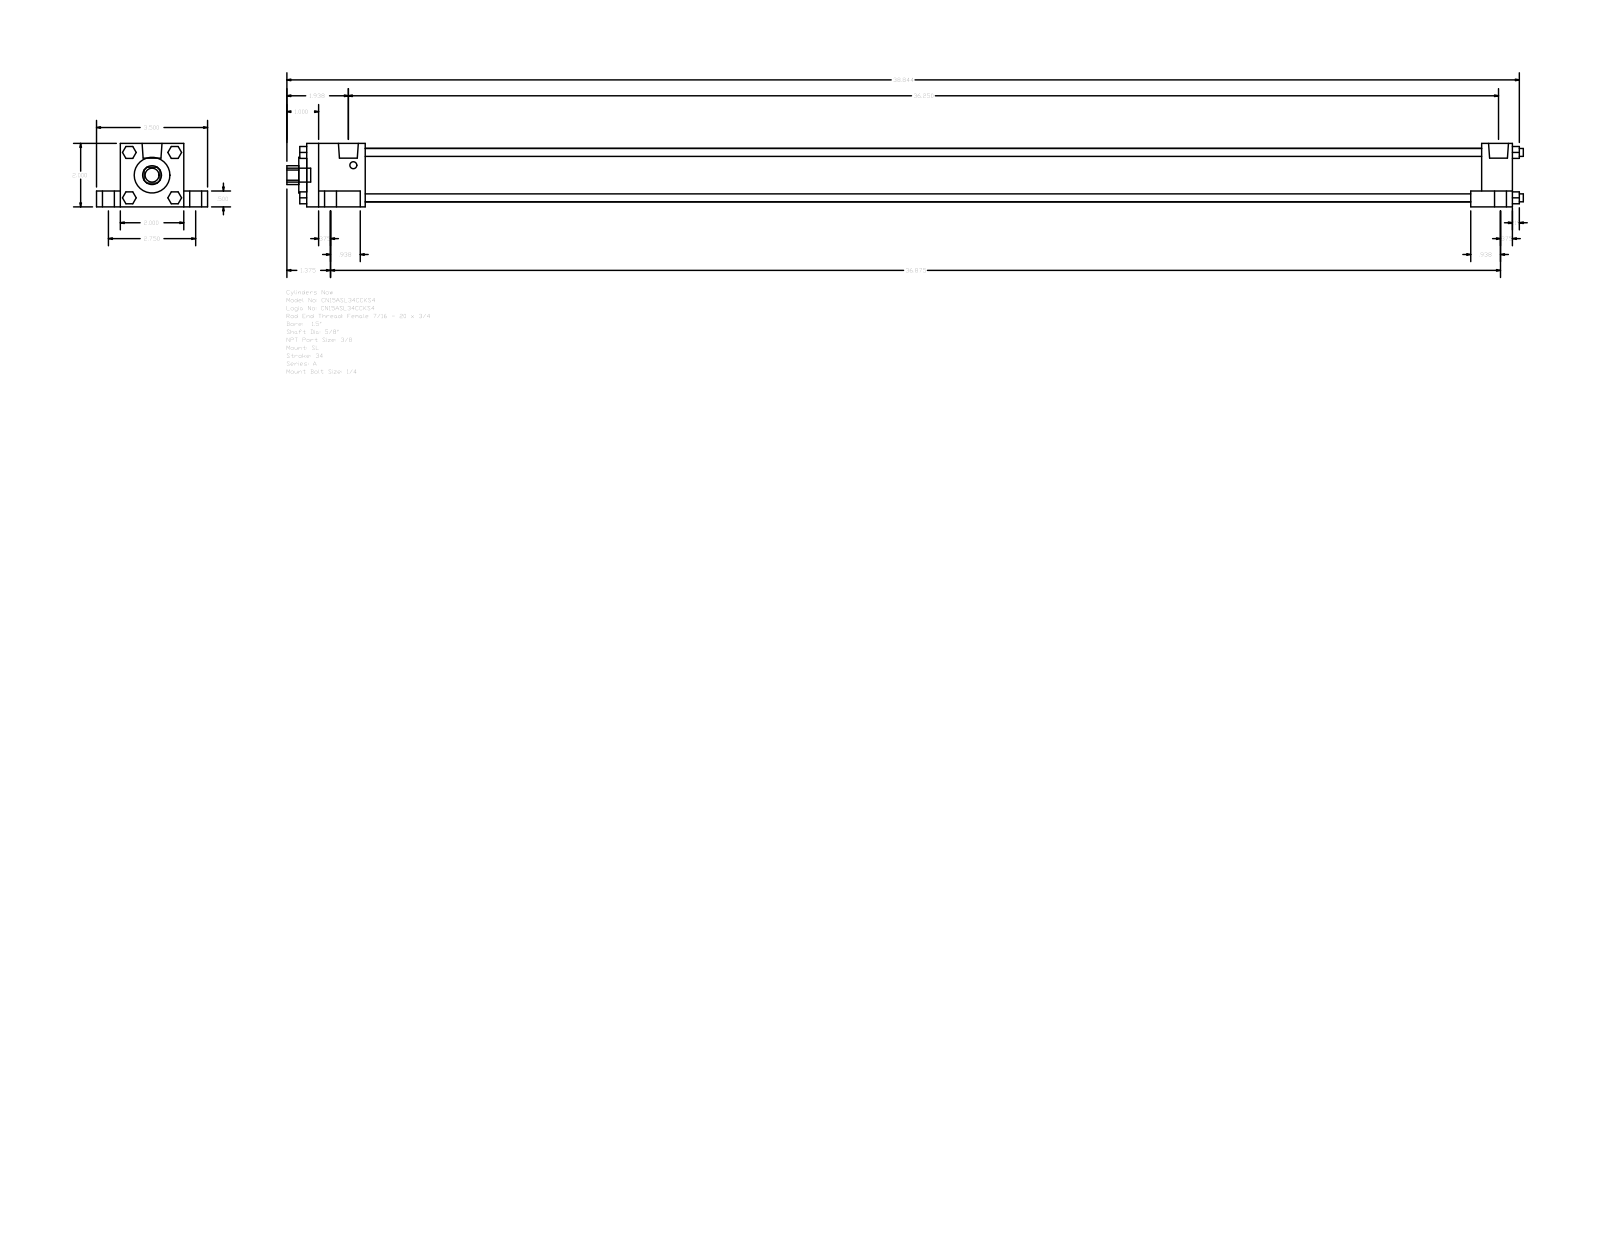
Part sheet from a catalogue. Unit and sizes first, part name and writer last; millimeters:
Units: millimetres
Overall size (bounding box): 989.81 × 88.9 × 50.8
Round holes (diameter × count): ⌀15.88 ×1, ⌀28.57 ×1, ⌀42.93 ×1
Round bosses / shafts (diameter × count): ⌀15.88 ×4, ⌀9.53 ×4, ⌀6.35 ×4, ⌀5.56 ×4, ⌀15.93 ×2, ⌀11.11 ×1
Partial cylindrical surfaces — rounded edges, fillets, slot ends (radius × count): R7.54 ×1
Main face-to-face distances: 50.8, 19.05, 12.7, 38.1, 69.85, 965.2, 9.52, 33.34, 940.59, 24.61
Bodies: 0 solids, 148 faces (112 planar, 36 cylindrical, 0 other)
Part name (STEP PRODUCT): A_SL__0150_0.625
STEP written by: GSSL Pune (CONFIG_CONTROL_DESIGN)
